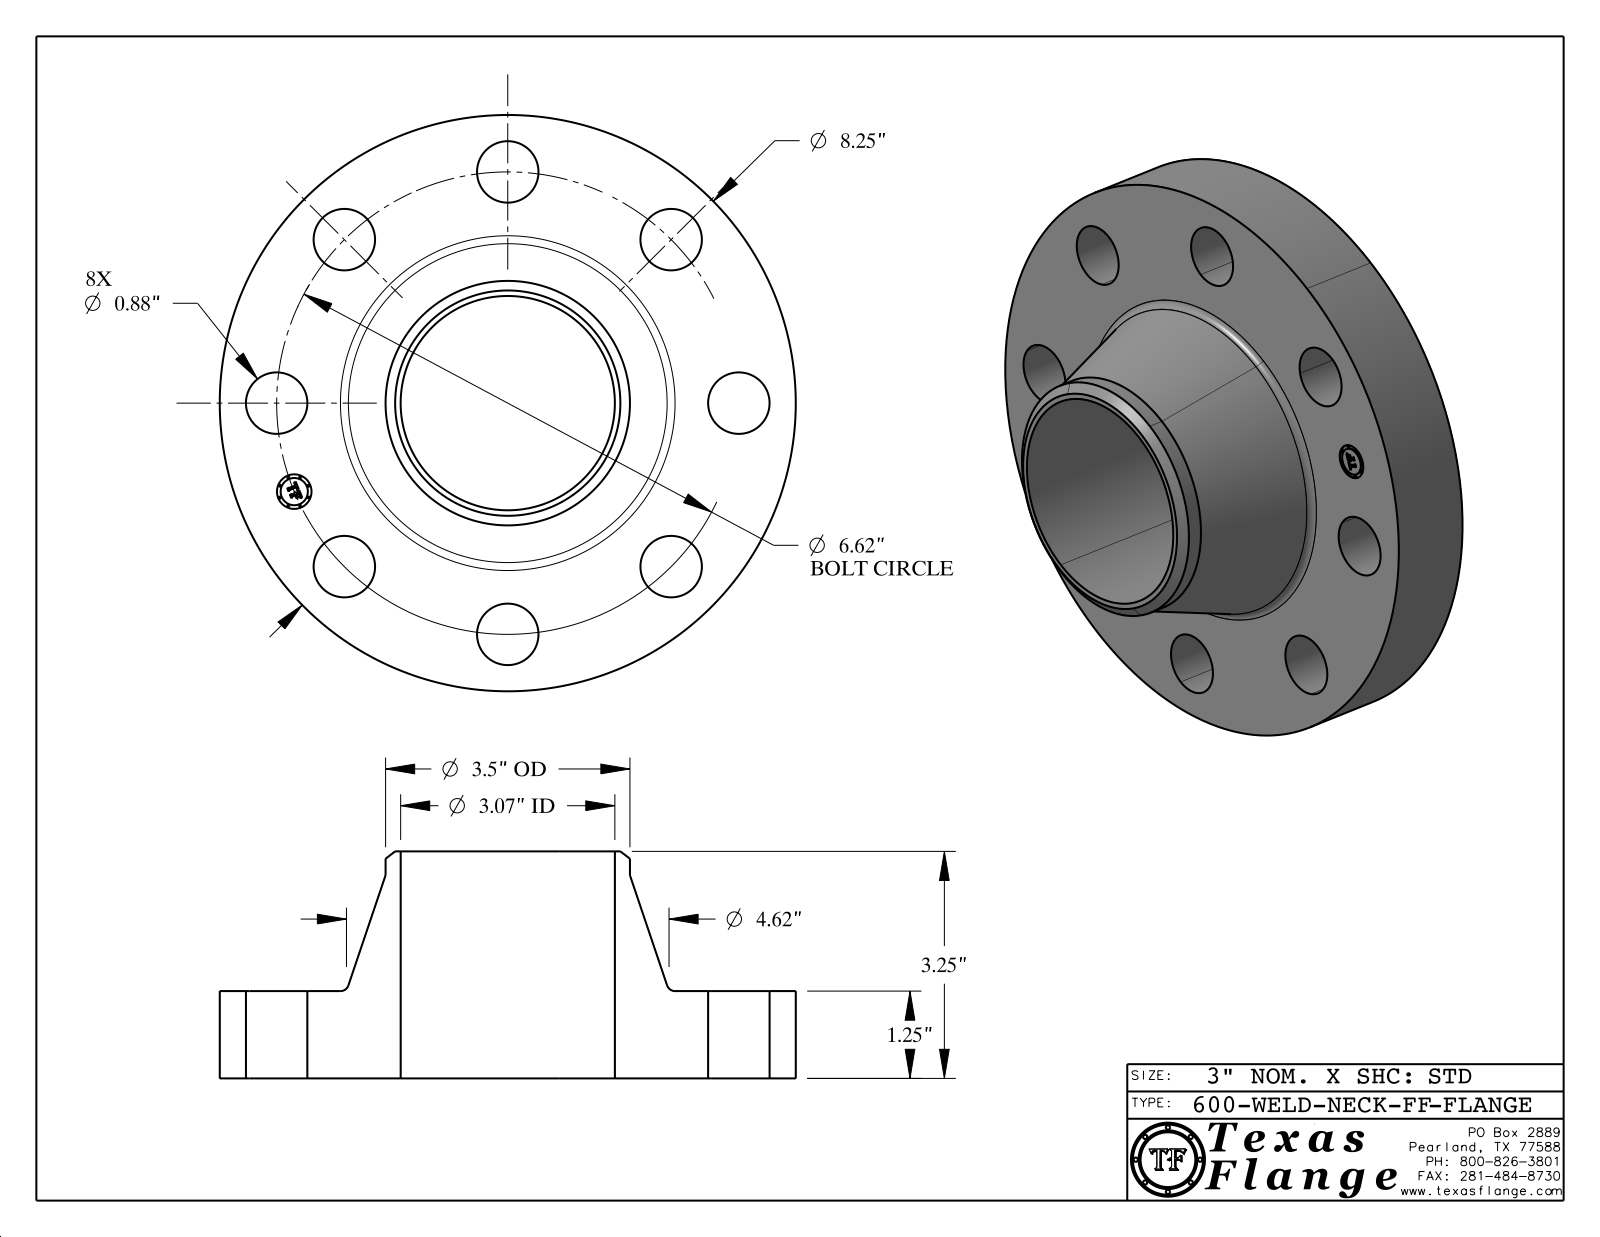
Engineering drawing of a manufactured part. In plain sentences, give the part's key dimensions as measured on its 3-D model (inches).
The part is named "600-WELD-NECK-FF". Its 3-D file was written by "CATIA V5 STEP AP214 (AUTOMOTIVE_DESIGN)". It is 1 solid with 416 faces: 368 planar, 42 cylindrical and 6 other. Overall it measures 8.25 by 8.25 by 3.25 inches. Its volume is 61.55 cubic inches and its surface area 191.7 square inches. Round holes: 8 of diameter 0.88, 1 of diameter 0.495, 1 of diameter 3.068. Round bosses or shafts: 8 of diameter 0.03, 1 of diameter 8.25, 1 of diameter 3.5, 1 of diameter 0.39. The main face-to-face distances are 1.25, 3.25, 2, 0.015, 1.235, 2.015, 0.148, 0.145, 0.027, 0.096. The hole center spacings are 3.31, 2.533, 6.116, 4.681, 4.681, 1.291, 3.678, 6.493.
